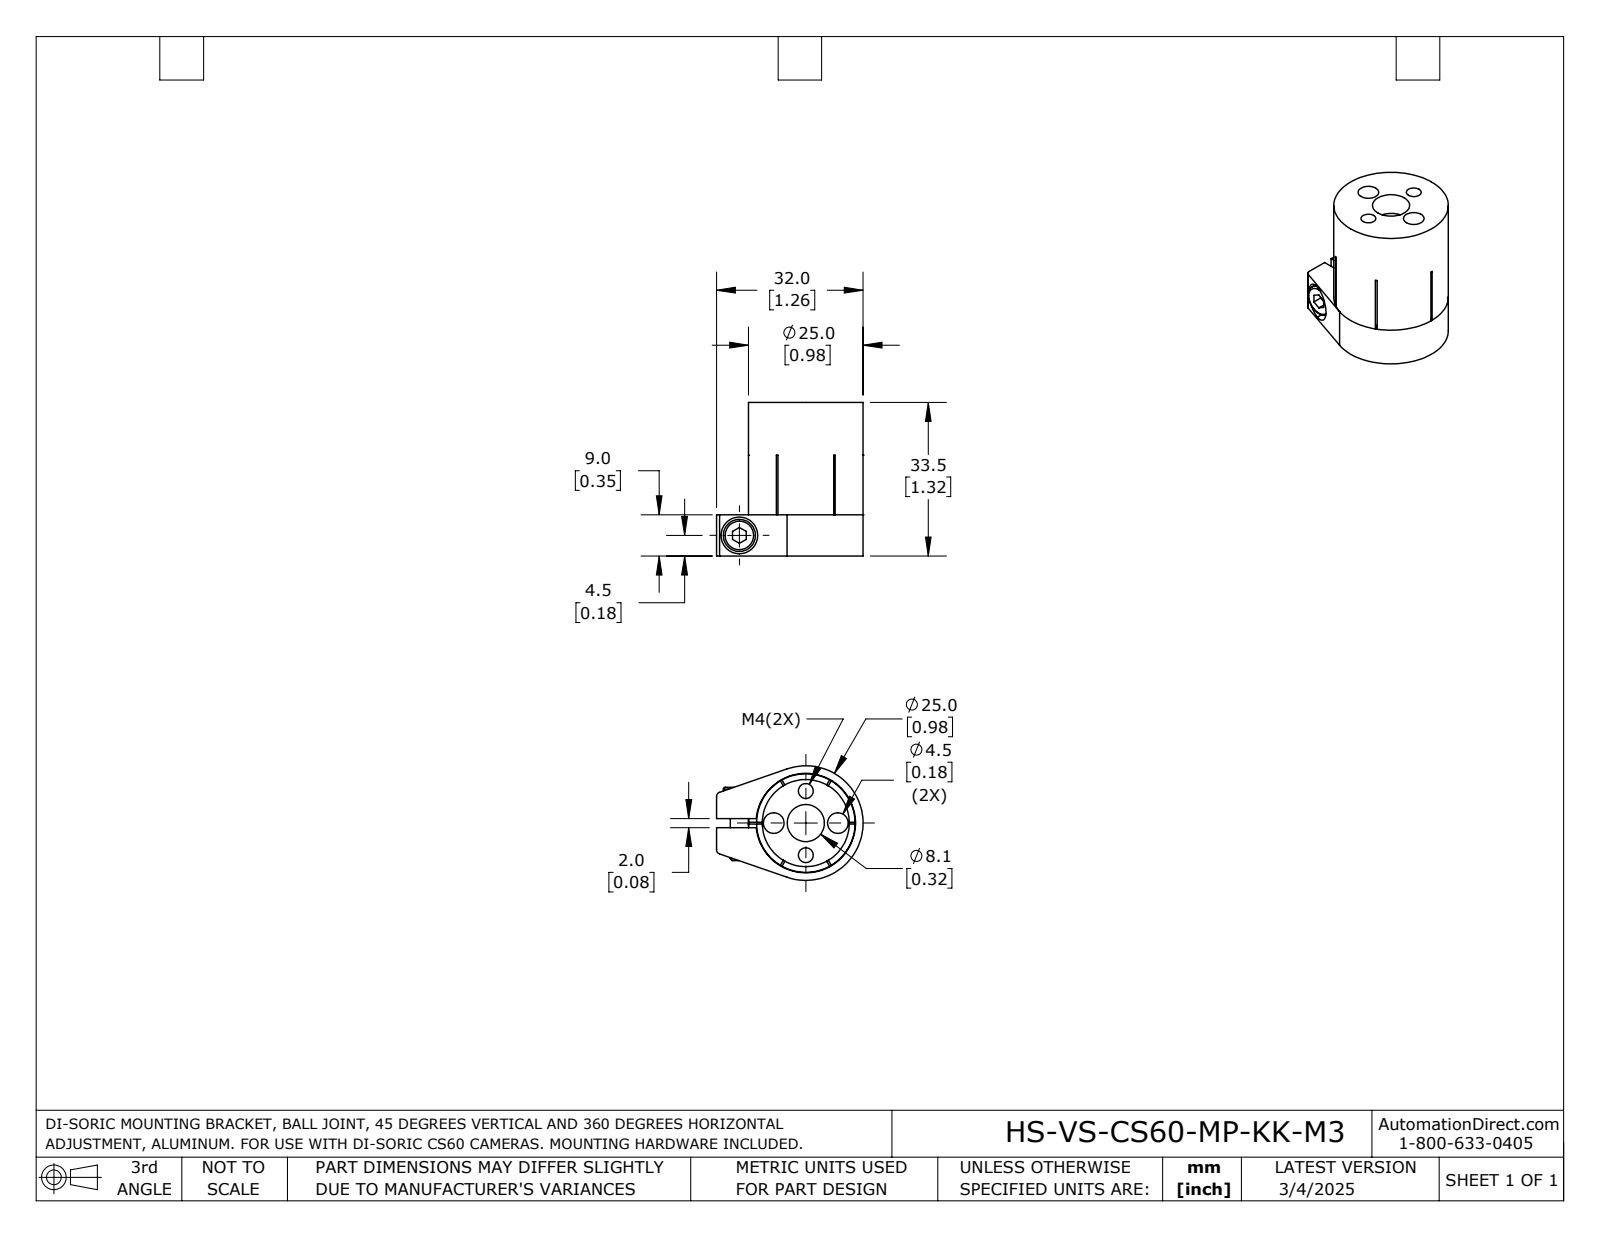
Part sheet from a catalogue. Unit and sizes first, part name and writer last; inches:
Units: inches
Overall size (bounding box): 1.319 × 1.26 × 0.984
Round holes (diameter × count): ⌀0.177 ×3, ⌀0.128 ×2, ⌀0.315 ×1, ⌀0.319 ×1, ⌀0.748 ×1, ⌀0.854 ×1
Round bosses / shafts (diameter × count): ⌀0.984 ×1, ⌀0.846 ×1, ⌀0.276 ×1, ⌀0.157 ×1
Partial cylindrical surfaces — rounded edges, fillets, slot ends (radius × count): R0.039 ×2
Main face-to-face distances: 1.319, 0.016, 0.197, 1.122, 0.965, 0.768, 0.354, 0.031, 0.047, 0.079
Hole centre spacings: 0.276, 0.39, 0.551
Volume: 0.526 in³ · Surface area: 12.84 in²
Bodies: 1 solid, 100 faces (71 planar, 23 cylindrical, 6 other)
Part name (STEP PRODUCT): HS-VS-CS60-MP-KK-M3
STEP written by: SolidWorks 2024 (AUTOMOTIVE_DESIGN)
